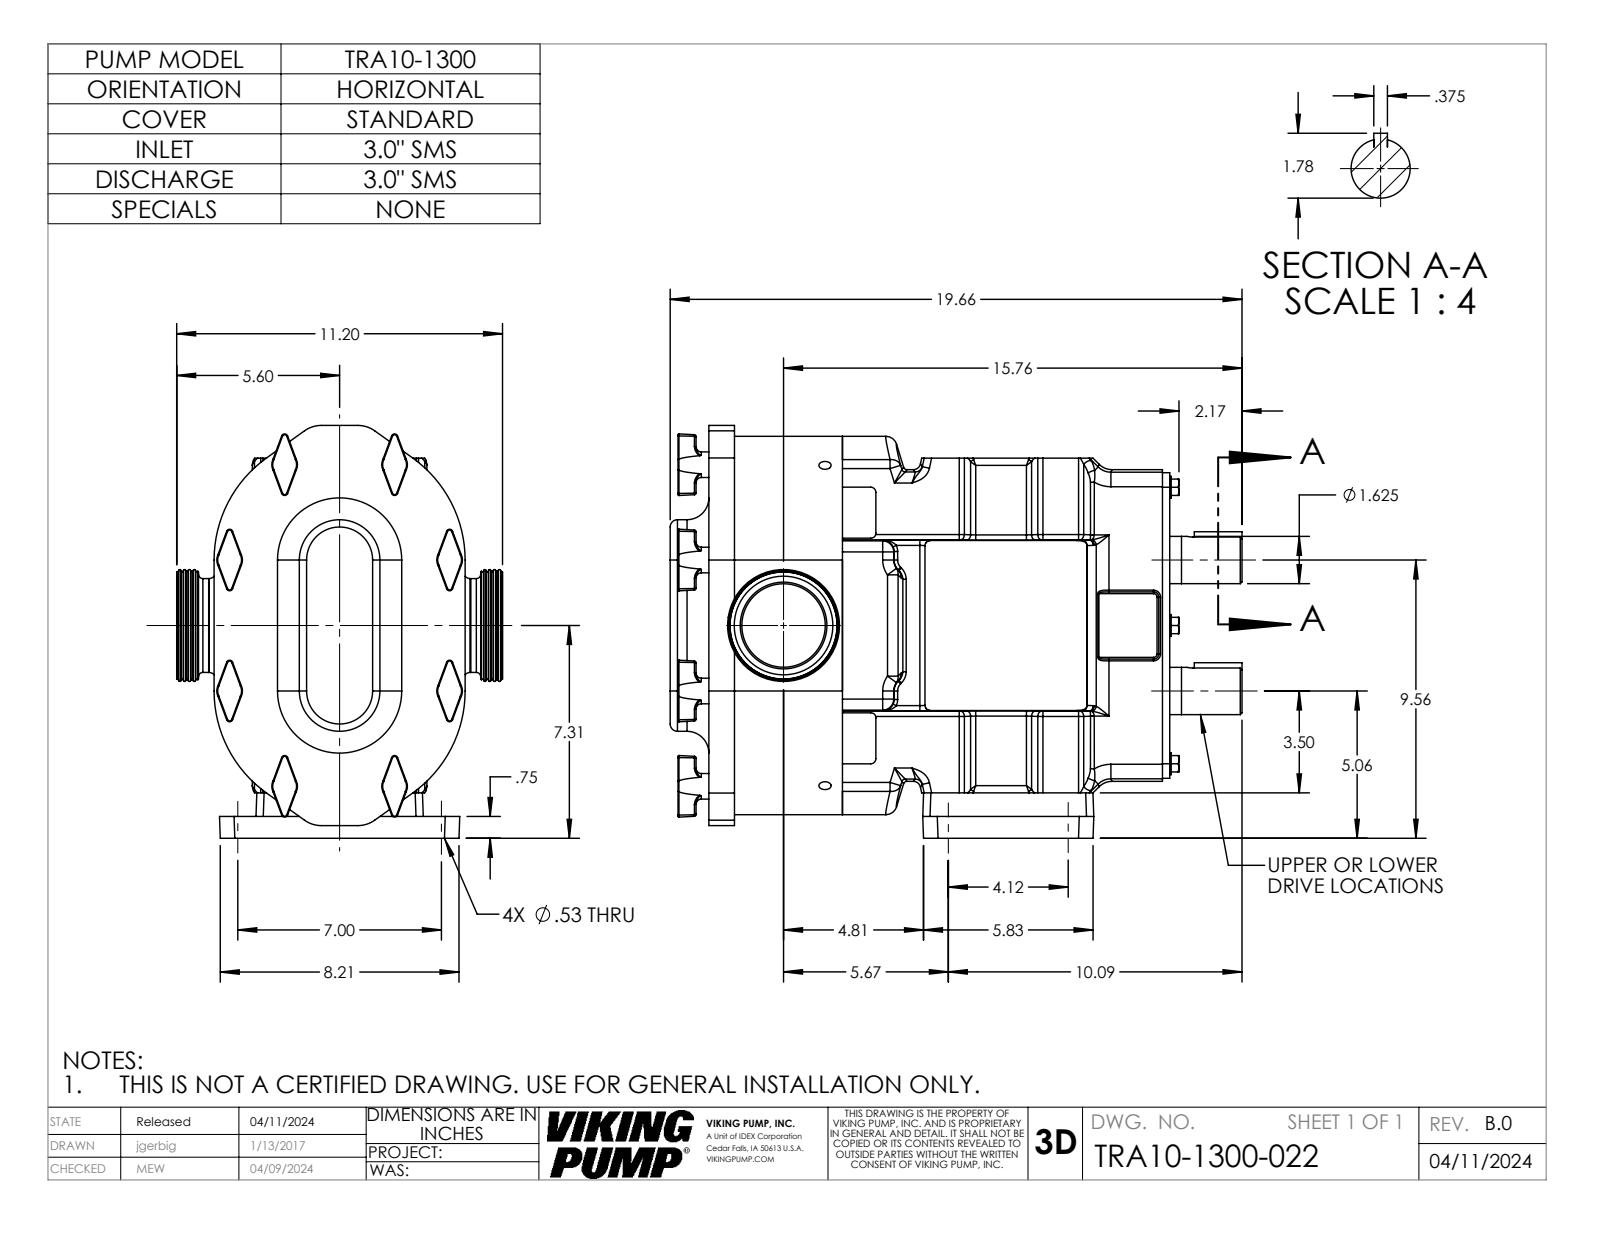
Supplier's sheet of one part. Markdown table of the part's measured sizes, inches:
| quantity | value |
| --- | --- |
| part name | TRA10-1300-BODY; TRA10-0600-GEARBOX-H; TRA10-0600-COVER-STD; 1300SMS30 (+1 more) |
| STEP written by | SolidWorks 2022 (AUTOMOTIVE_DESIGN) |
| units | inches |
| bodies | 5 solids, 1163 faces (291 planar, 384 cylindrical, 488 other) |
| overall size | 19.656 × 14.185 × 11.2 |
| volume | 1 279 in³ |
| surface area | 1 410 in² |
| round holes (diameter × count) | 0.332 × 4, 0.531 × 4, 2.868 × 1, 3.39 × 1 |
| round bosses / shafts (diameter × count) | 0.88 × 8, 0.75 × 6, 1.624 × 2, 3.224 × 1, 2.982 × 1 |
| partial cylindrical surfaces (radius × count) | 0.18 × 44, 0.06 × 43, 0.03 × 32, 0.25 × 32, 0.38 × 28, 0.12 × 24, 0.5 × 20, 0.375 × 12 |
| main face-to-face distances | 3.712, 0.5, 0.88, 4.592, 0.36, 15.842, 14.962, 11.25, 6.5, 0.75 |
| hole center spacings | 2.895, 4.12, 7, 8.122 |
